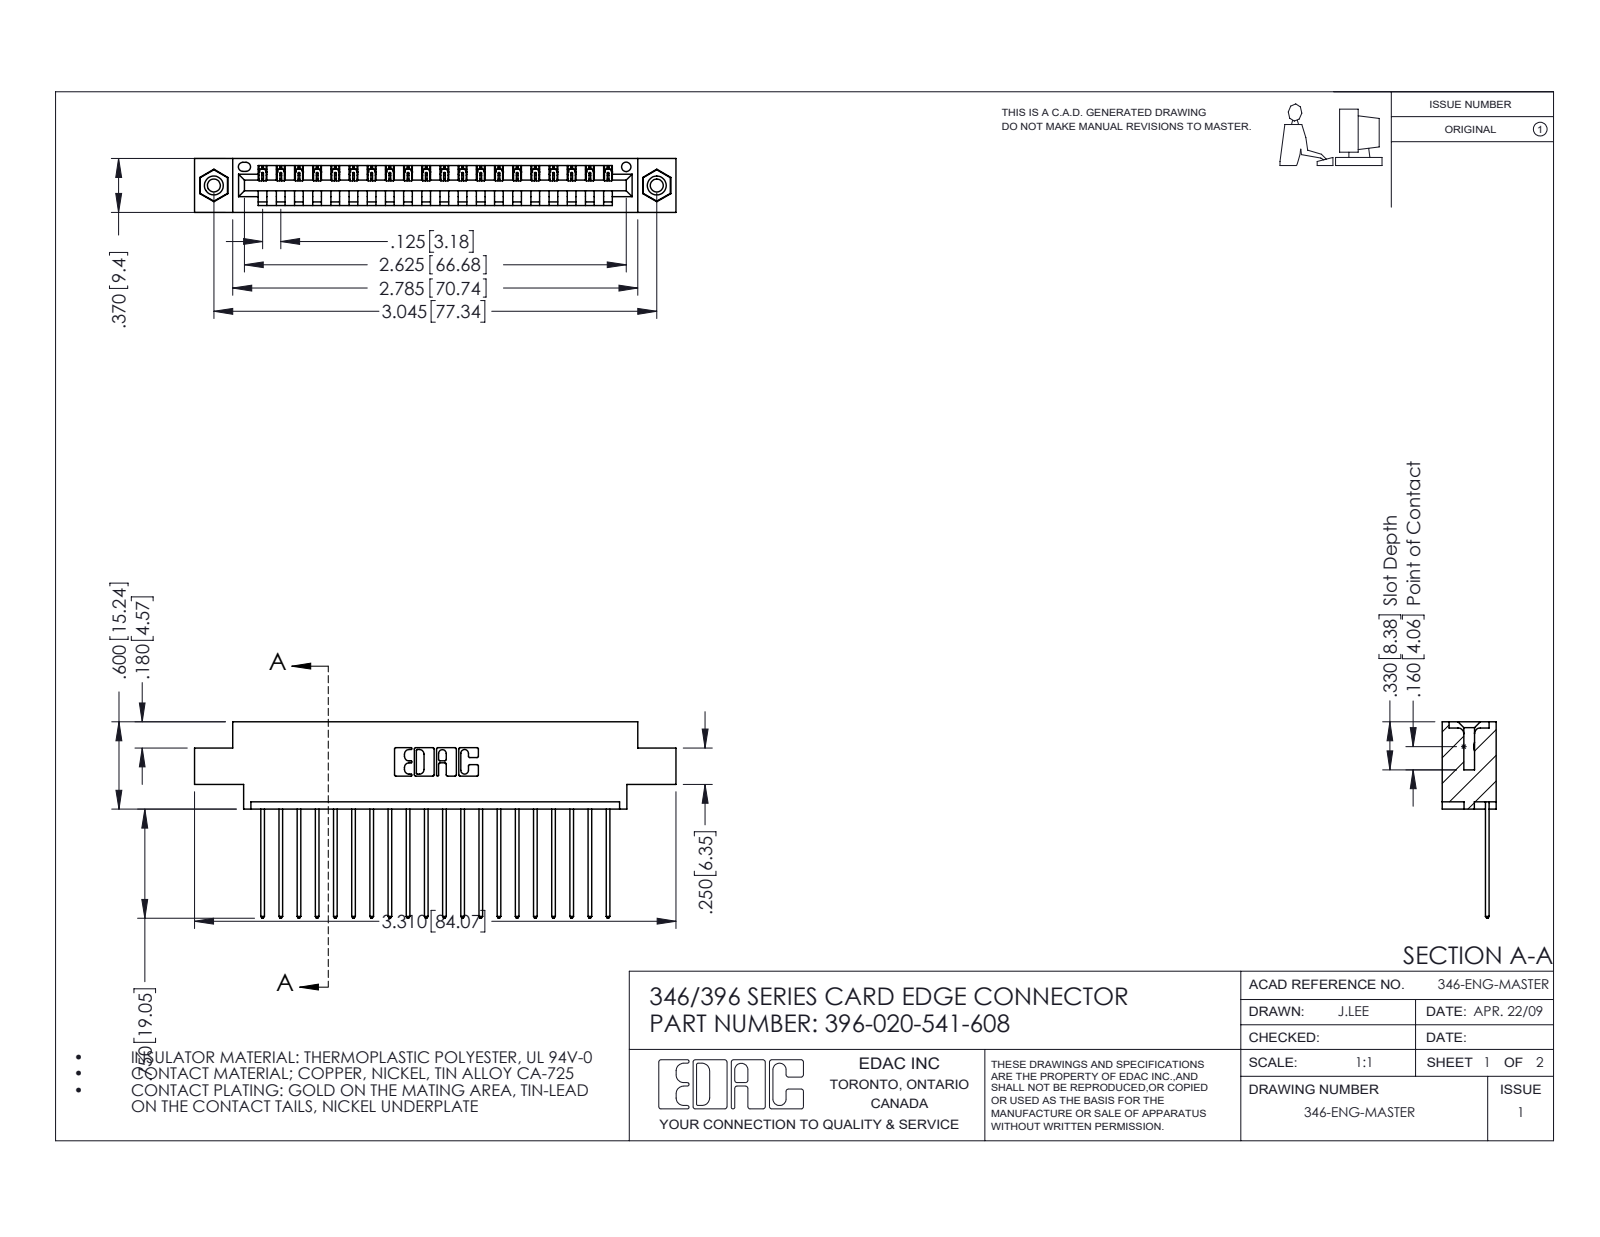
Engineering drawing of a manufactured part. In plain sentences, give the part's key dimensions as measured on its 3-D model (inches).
The part is named "396-020-541-608; 346 Part_0.170 Offset - 0.156 Dia-TI; 345-250-001_345-250-003-102; 345-292-001_345-293-141". Its 3-D file was written by "SolidWorks 2016 (CONFIG_CONTROL_DESIGN)". It is 23 solids with 1346 faces: 912 planar, 418 cylindrical and 16 other. Overall it measures 3.31 by 1.35 by 0.37 inches. Its volume is 0.476 cubic inches and its surface area 15.64 square inches. Round holes: 2 of diameter 0.089, 2 of diameter 0.125, 2 of diameter 0.156, 1 of diameter 0.064. Round bosses or shafts: 2 of diameter 0.155. Partial cylindrical surfaces (rounded edges, fillets, slot ends): 40 of radius 0.006, 40 of radius 0.01, 22 of radius 0.01, 6 of radius 0.007, 6 of radius 0.031, 3 of radius 0.026, 2 of radius 0.031, 2 of radius 0.04. The main face-to-face distances are 0.048, 0.322, 0.37, 0.25, 0.072, 0.298, 0.025, 0.222, 0.148, 0.1. The hole center spacings are 0.246, 2.837, 3.045.
